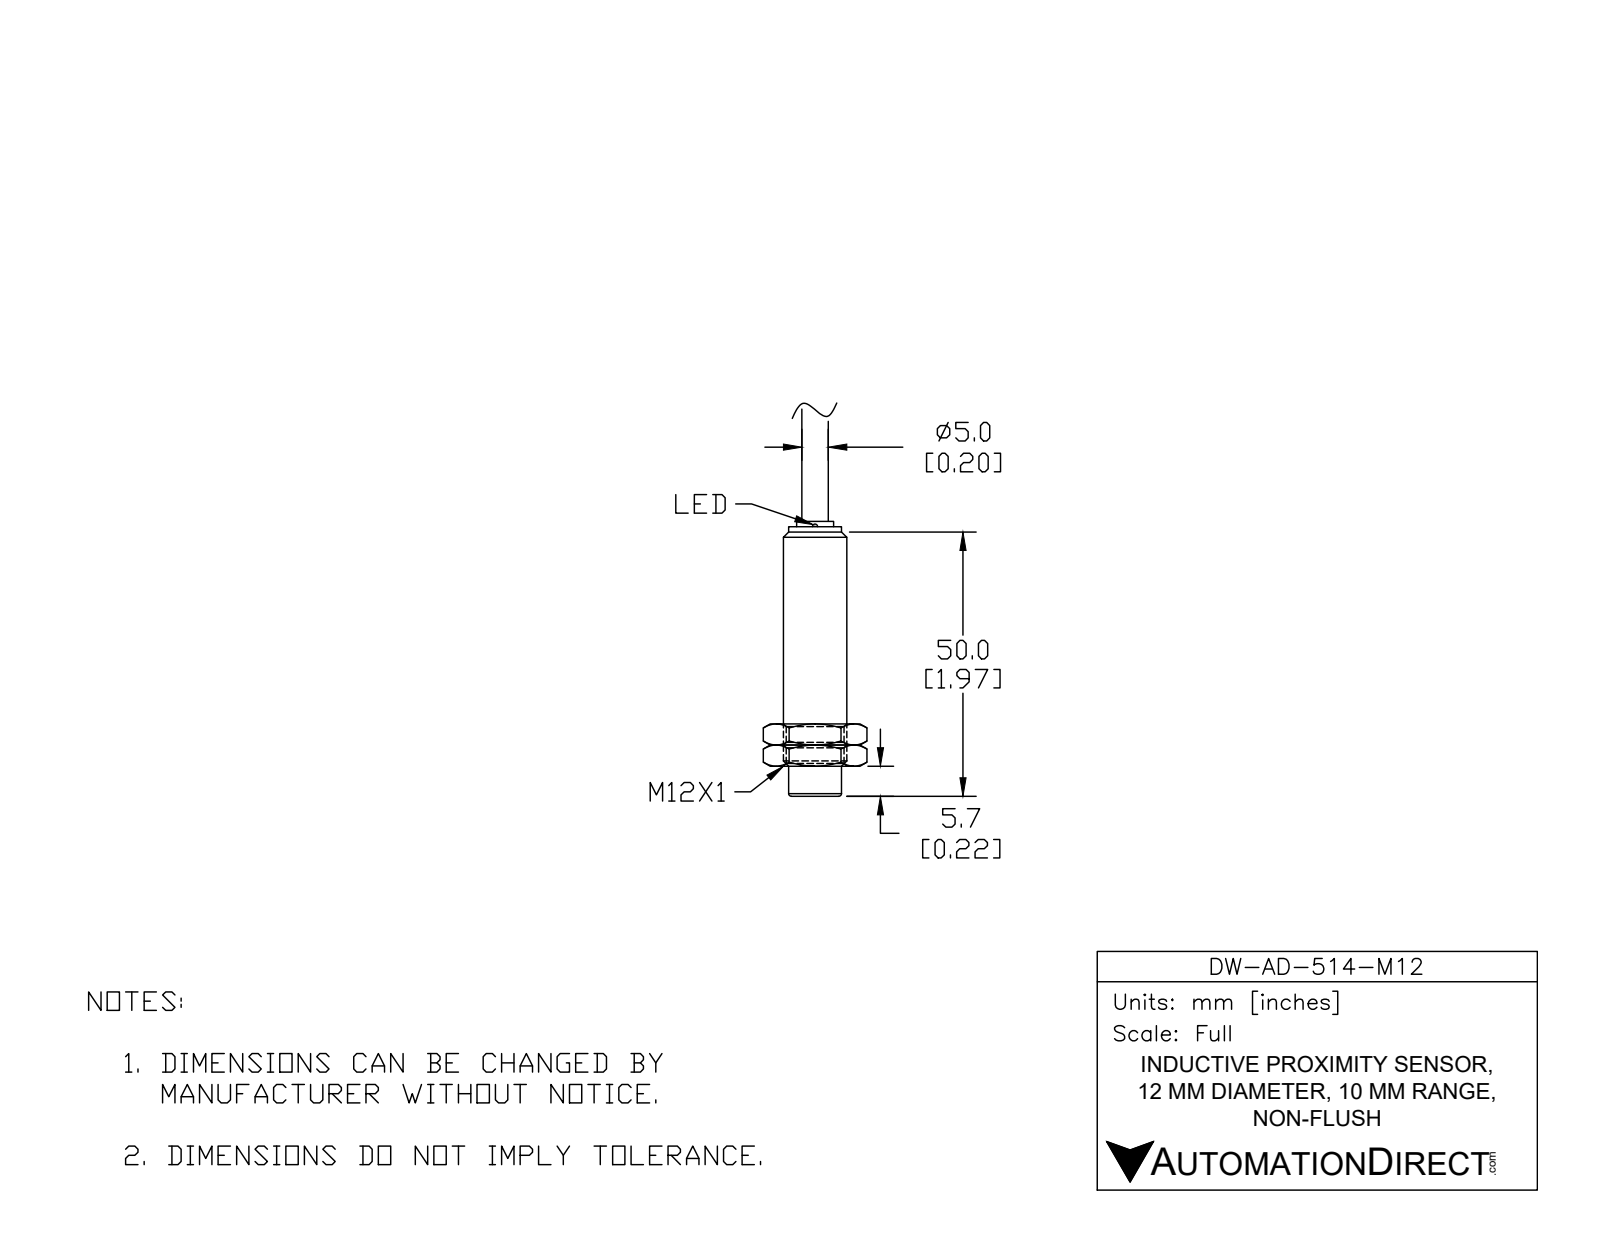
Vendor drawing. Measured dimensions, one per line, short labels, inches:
name: DW-AD-514-M12
written by: SolidWorks 2017 (AUTOMOTIVE_DESIGN)
unit: in
bodies: 1 solid, 30 faces (15 planar, 5 cylindrical, 10 other)
size: 2.976 × 0.472 × 0.472
volume: 0.369 in³; area: 3.799 in²
bosses: 1× ⌀0.472, 1× ⌀0.421, 1× ⌀0.413, 1× ⌀0.268, 1× ⌀0.197
face distances: 2, 2.047, 0.047, 2.031, 0.031, 0.016
